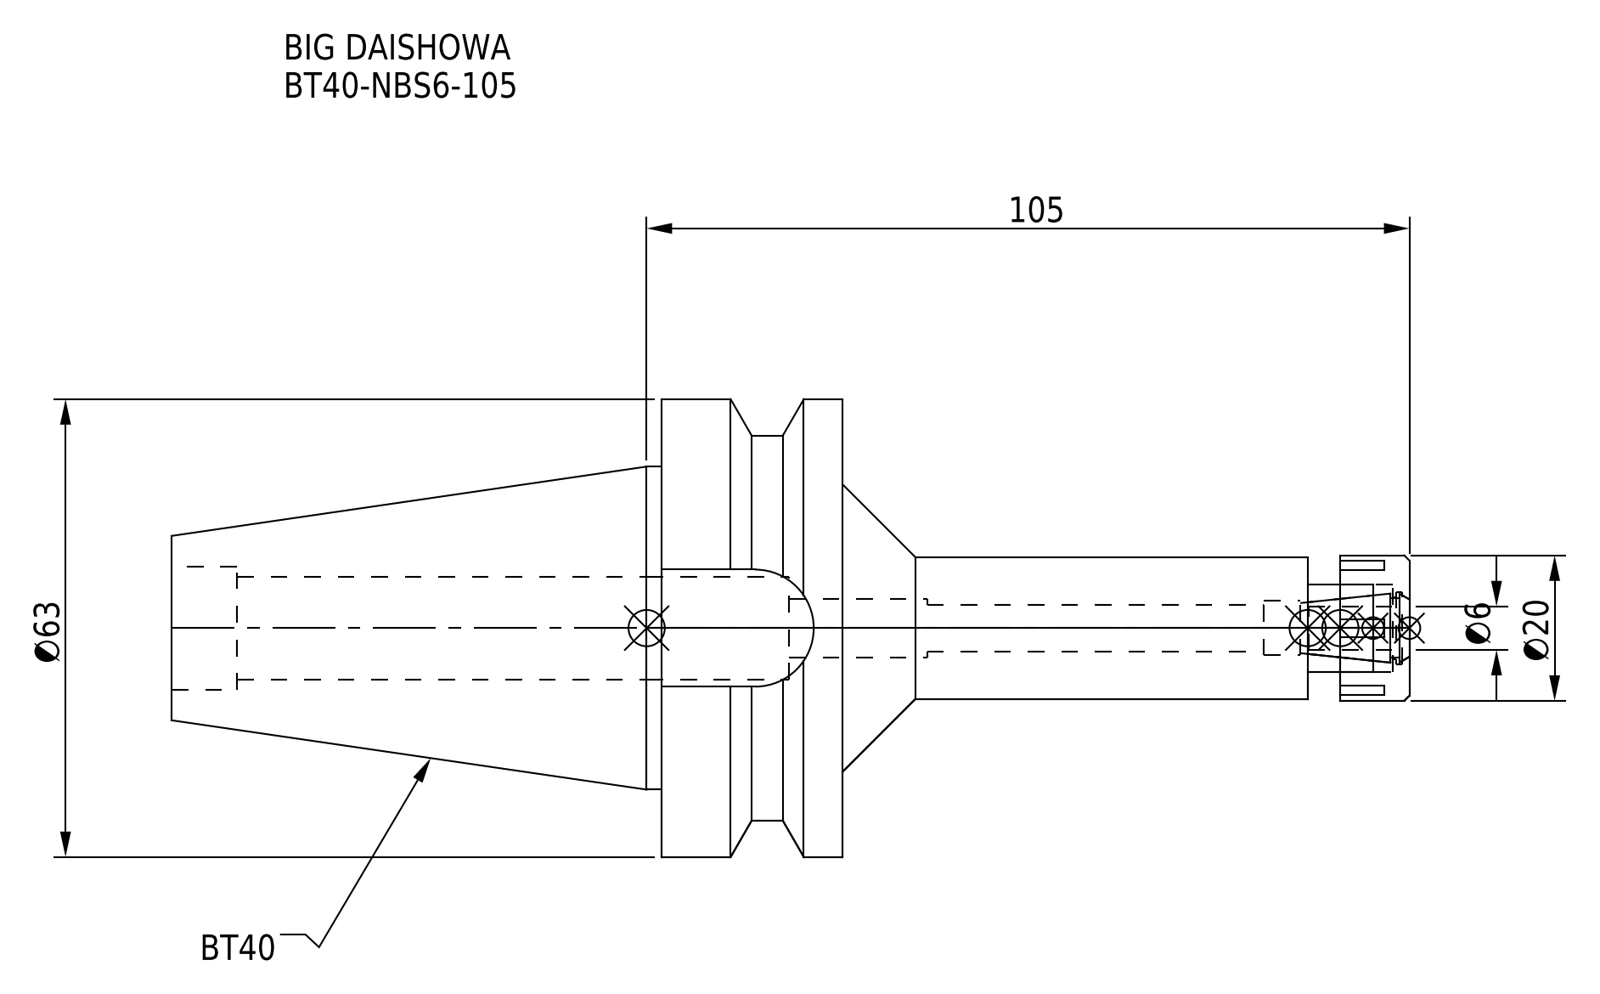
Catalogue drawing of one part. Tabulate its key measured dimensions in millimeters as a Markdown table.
| quantity | value |
| --- | --- |
| part name | DXF_TEMP_ASSY_ASM_4_ASM.stp; BT40NB06105-060_ASM.stp; BT40-NBS6-105; BT40-NBS6-105_1.stp (+3 more) |
| STEP written by | SolidWorks 2019 (CONFIG_CONTROL_DESIGN) |
| units | millimeters |
| bodies | 2 solids, 93 faces (45 planar, 34 cylindrical, 14 other) |
| overall size | 170.4 × 63 × 63 |
| volume | 143 163 mm³ |
| surface area | 29 899 mm² |
| round holes (diameter × count) | 6.4 × 1, 7.5 × 1, 8 × 1, 8.5 × 1, 10 × 1, 12 × 1, 14.2 × 1, 17 × 1 |
| round bosses / shafts (diameter × count) | 63 × 1, 53 × 1, 44.45 × 1, 20 × 1, 19.5 × 1 |
| partial cylindrical surfaces (radius × count) | 8.05 × 1 |
| main face-to-face distances | 25, 45, 92.4, 67.4, 156.4, 4.5, 78, 103, 170.4, 14 |
